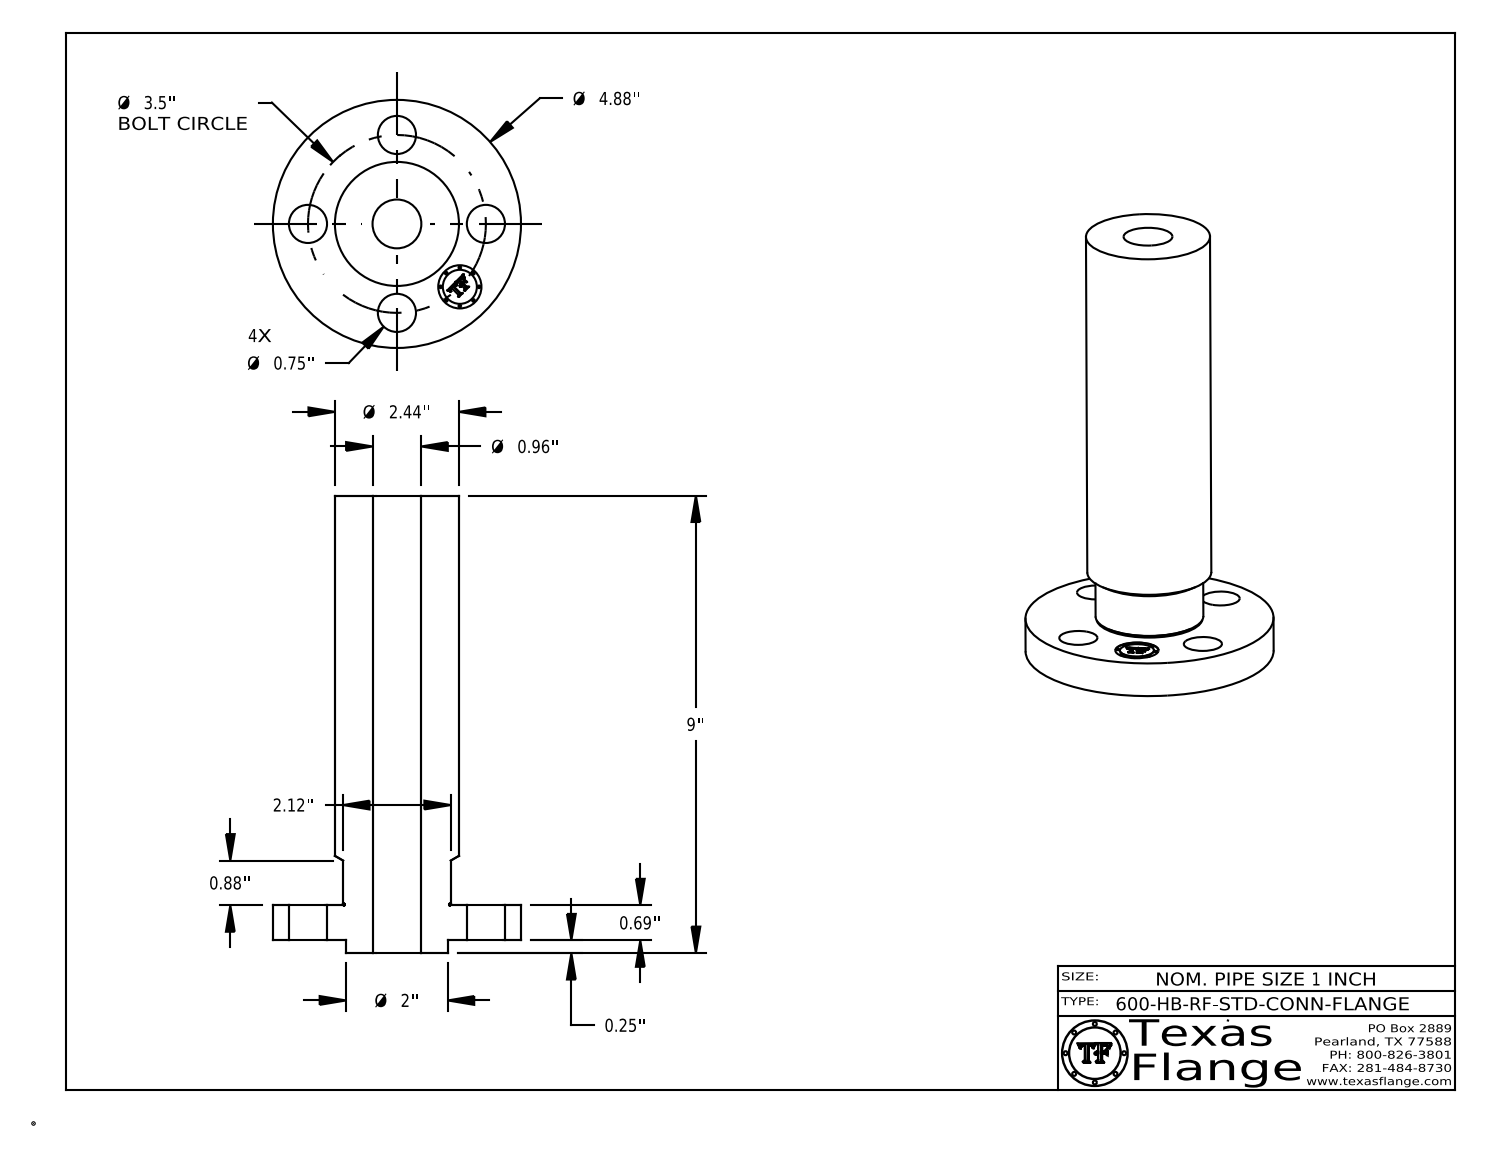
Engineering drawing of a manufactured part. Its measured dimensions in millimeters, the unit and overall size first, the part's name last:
Units: millimetres
Overall size (bounding box): 228.6 × 124 × 124
Round holes (diameter × count): ⌀19.1 ×4, ⌀21.6 ×1, ⌀24.4 ×1
Round bosses / shafts (diameter × count): ⌀1.3 ×8, ⌀124 ×1, ⌀62 ×1, ⌀53.8 ×1, ⌀50.8 ×1, ⌀17 ×1
Main face-to-face distances: 17.5, 222.3, 204.7, 6.4, 23.9, 228.6, 23.7, 17.4, 204.9, 0.4
Hole centre spacings: 44.5, 62.9, 34, 82.1, 88.9
Volume: 697 800 mm³ · Surface area: 91 100 mm²
Bodies: 1 solid, 413 faces (369 planar, 38 cylindrical, 6 other)
Part name (STEP PRODUCT): 1-600-HB-RF-STD-CONN-FLANGE
STEP written by: CATIA V5 STEP AP214 (AUTOMOTIVE_DESIGN)
